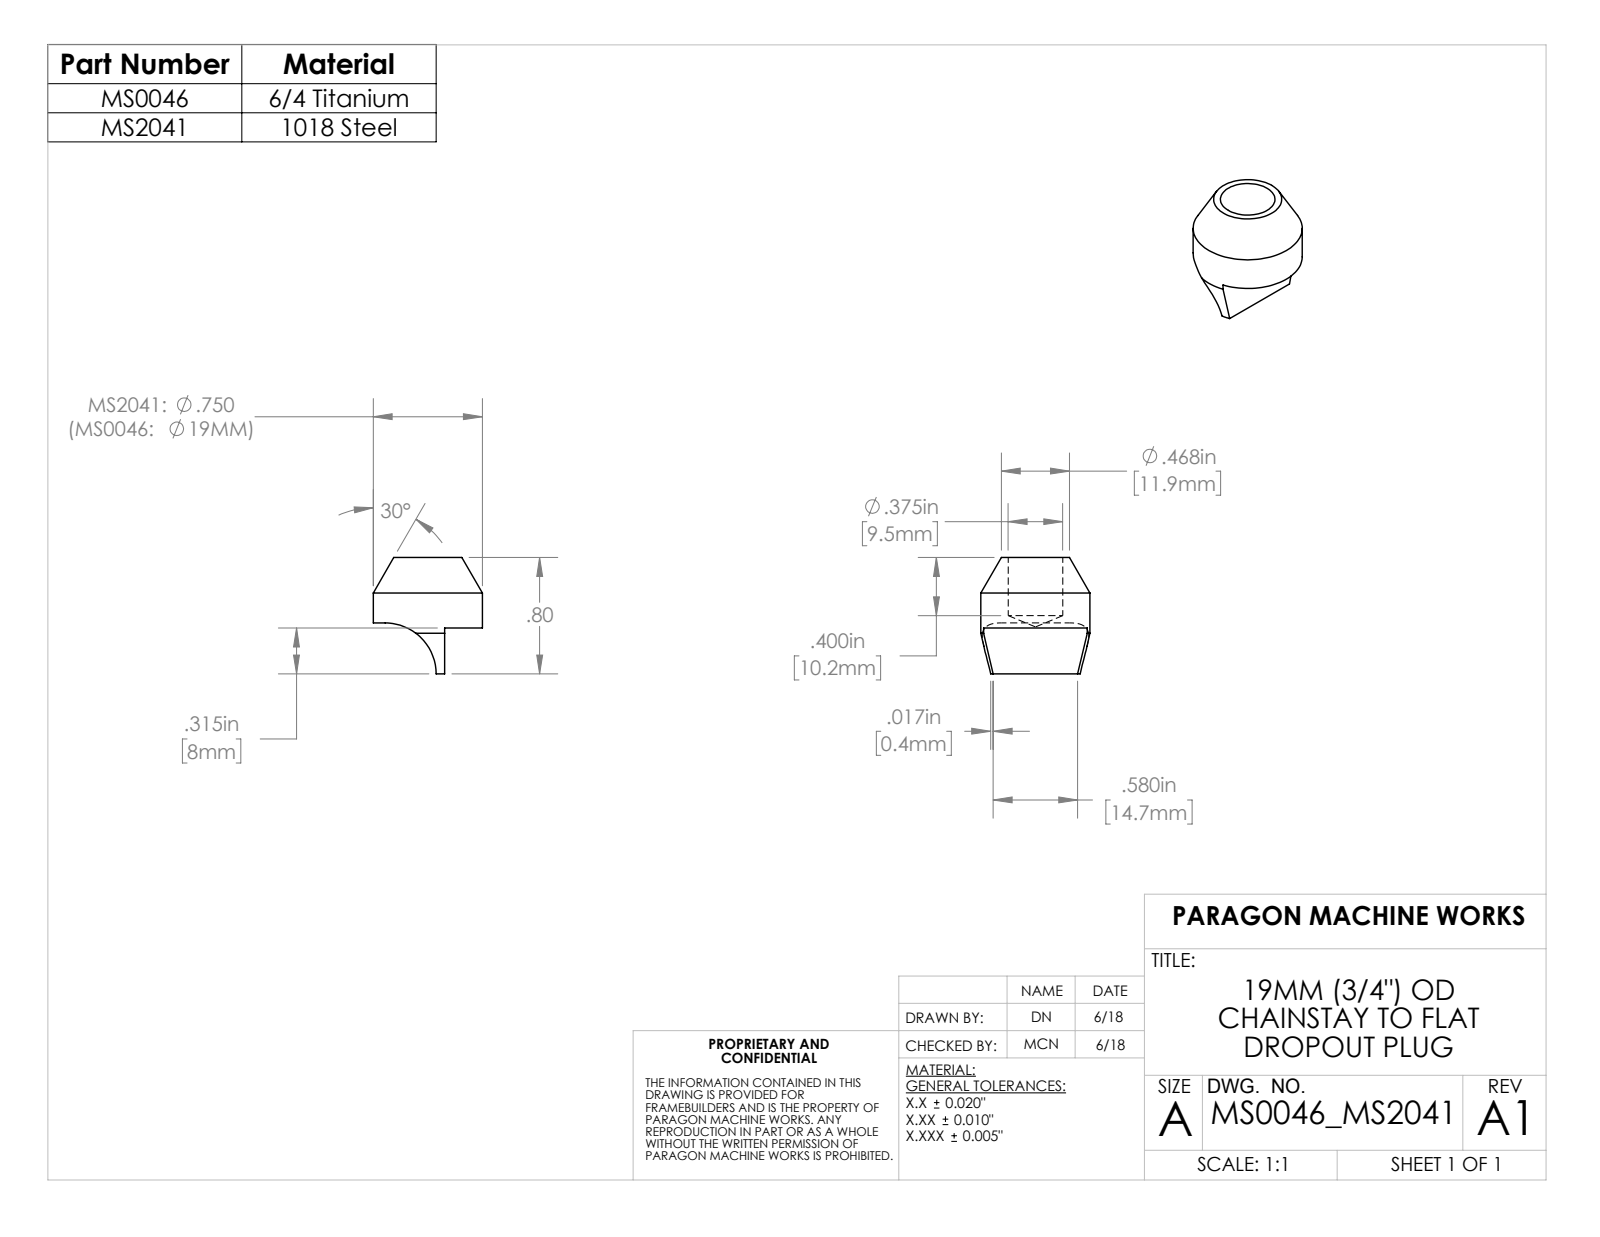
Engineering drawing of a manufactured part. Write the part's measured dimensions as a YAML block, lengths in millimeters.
part_name: "MS2041"
step_written_by: "SolidWorks 2023 (AUTOMOTIVE_DESIGN)"
units: millimeters
bodies: {solids: 1, faces: 17, planar: 5, cylindrical: 5, other: 7}
overall_size: [20.3, 19.1, 19.1]
volume: 2520
surface_area: 1663
round_holes:
  - {diameter: 9.5, count: 1}
round_bosses_or_shafts:
  - {diameter: 19.1, count: 1}
partial_cylinders:
  - {radius: 8.9, count: 1}
face_to_face_distances: [12.3, 8, 20.3, 8.9, 0.9, 11.4]
